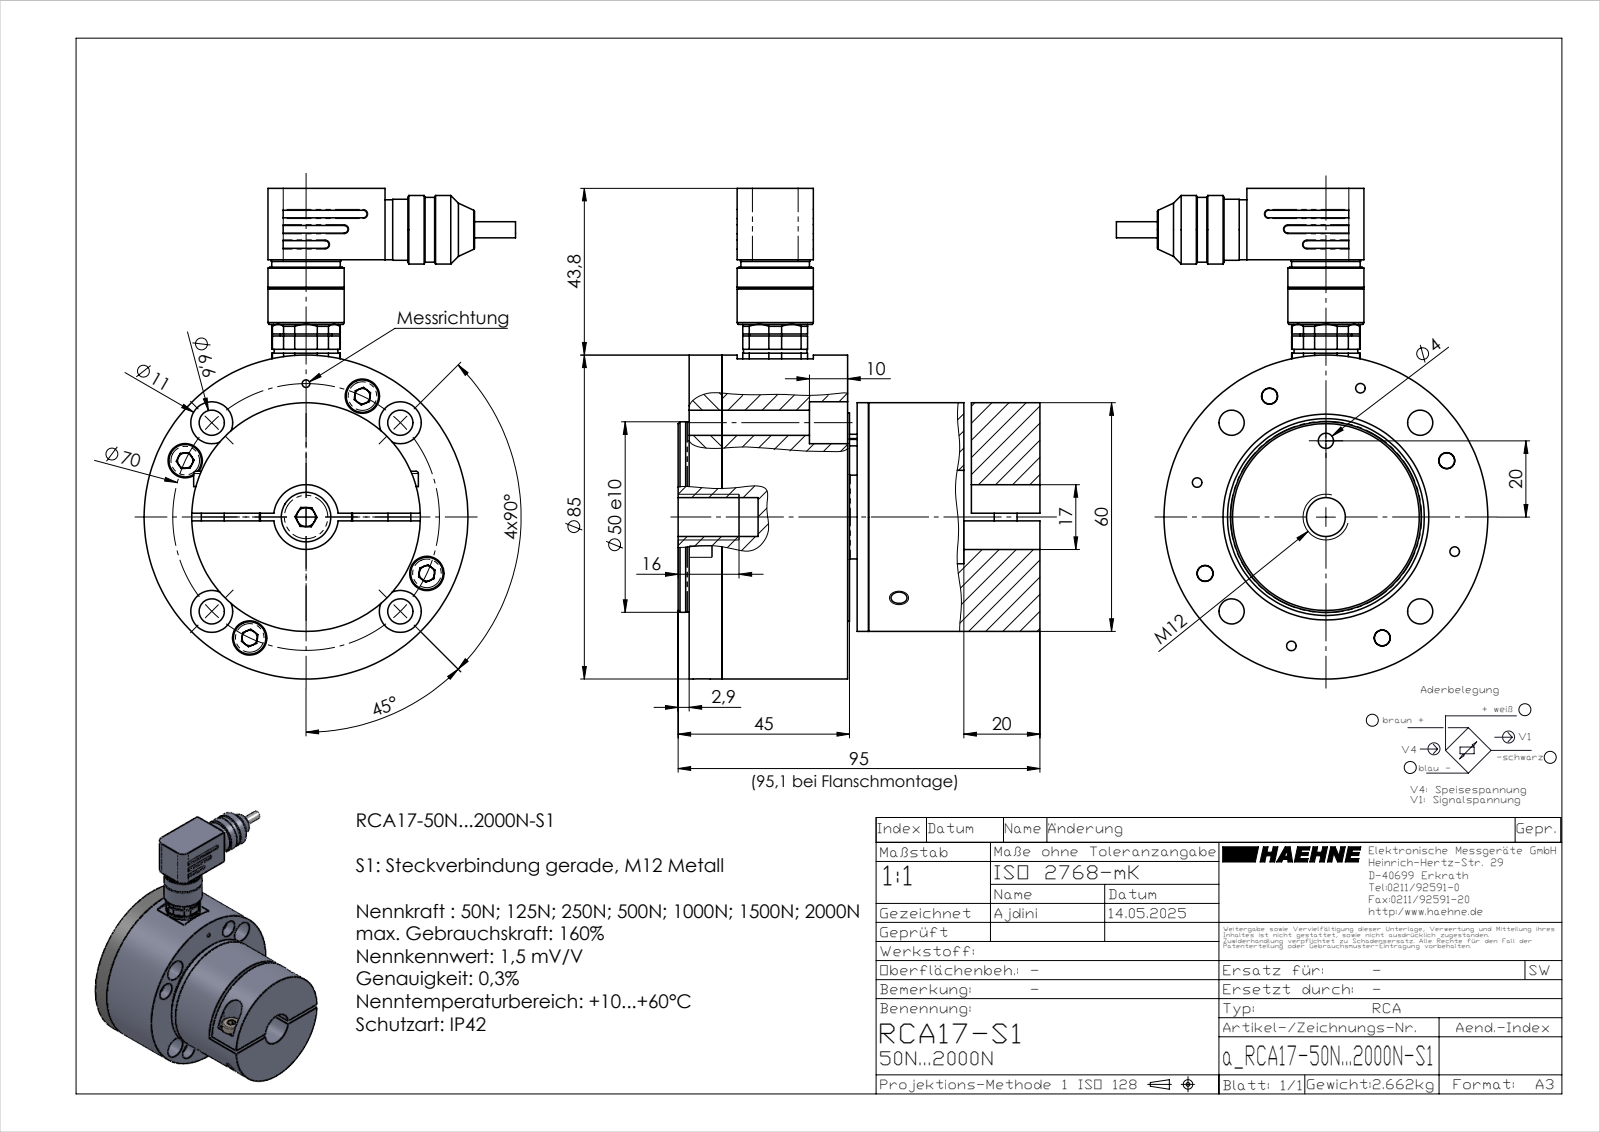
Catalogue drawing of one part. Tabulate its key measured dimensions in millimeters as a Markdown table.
| quantity | value |
| --- | --- |
| part name | inafag_1203-tvh_7zkvytp7yxkimpdvw8sj0b5w4_21; Washer DIN 9021 - 8.4_Washer DIN 9021 - 8.4; inafag_1203-tvh_7zkvytp7yxkimpdvw8sj0b5w4_01; inafag_1203-tvh_7zkvytp7yxkimpdvw8sj0b5w4_24 (+8 more) |
| STEP written by | SolidWorks 2023 (AUTOMOTIVE_DESIGN) |
| units | millimeters |
| bodies | 55 solids, 809 faces (409 planar, 228 cylindrical, 172 other) |
| overall size | 128.75 × 97.48 × 95.1 |
| volume | 385 480 mm³ |
| surface area | 116 784 mm² |
| round holes (diameter × count) | 3.4 × 9, 2.5 × 8, 6.6 × 6, 4.2 × 5, 4 × 4, 5.3 × 4, 9 × 4, 11 × 4, 4.5 × 2, 5 × 2, 2 × 1, 6 × 1 |
| round bosses / shafts (diameter × count) | 3 × 9, 5.7 × 8, 8.5 × 4, 5 × 4, 1.5 × 4, 1 × 4, 18 × 2, 16 × 2 |
| partial cylindrical surfaces (radius × count) | 0.2 × 12, 1 × 11, 0.3 × 6, 4 × 2, 5.5 × 2, 0.57 × 1, 0.65 × 1, 0.77 × 1 |
| main face-to-face distances | 2, 3, 8.6, 47.1, 35.5, 45, 11.6, 30, 50, 50.1 |
| hole center spacings | 35, 49.5, 24.78, 25.2, 32.8, 51.14, 56.46, 6 |
